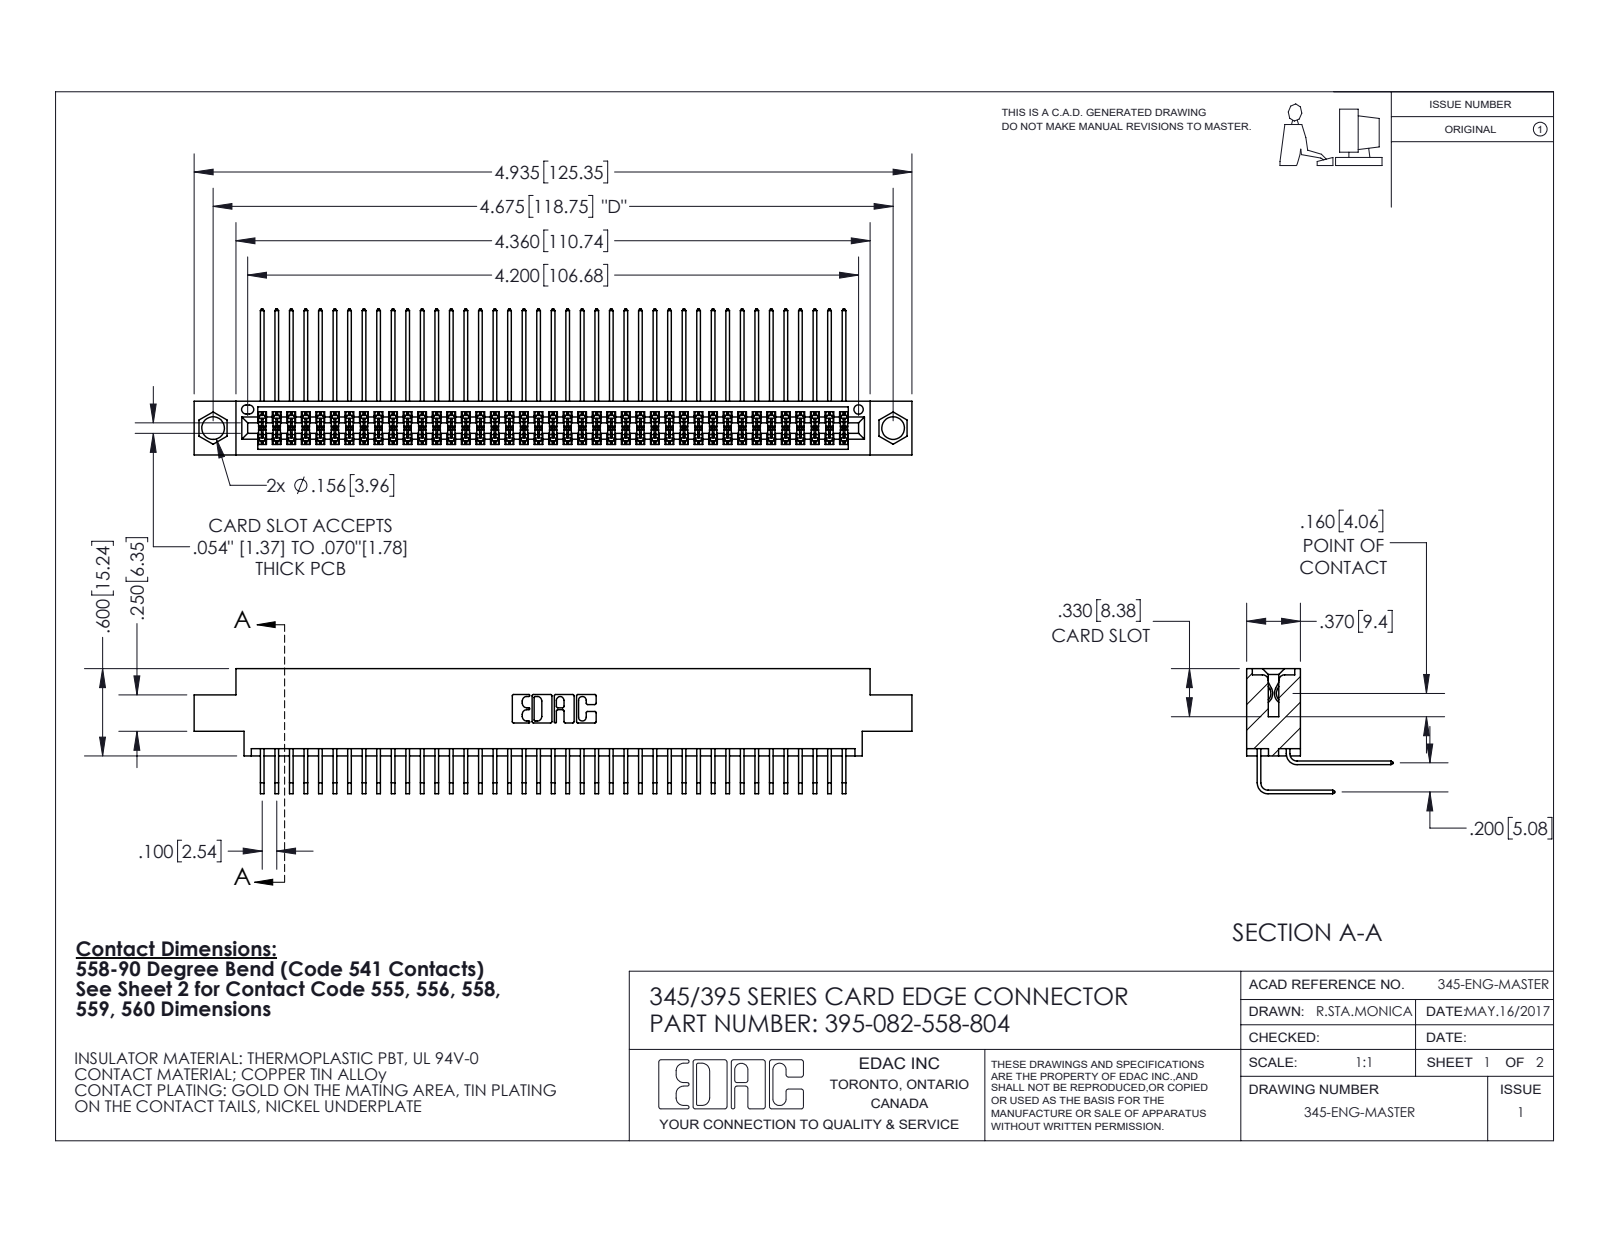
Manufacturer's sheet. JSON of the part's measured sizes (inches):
{"part_name": "345-292-001_558 559 Tail - 1; 395-082-558-804; 345 Part_0.170 Offset - 0.156 Dia-TI; 345-292-001_558 Tail - 2", "step_written_by": "SolidWorks 2020 (CONFIG_CONTROL_DESIGN)", "units": "inches", "bodies": {"solids": 83, "faces": 4408, "planar": 2968, "cylindrical": 1440, "other": 0}, "overall_size": [4.935, 1.005, 0.859], "volume_in3": 0.758, "surface_area_in2": 31.87, "round_holes": [[0.156, 2], [0.064, 1]], "partial_cylinders_radius": [[0.006, 123], [0.01, 22], [0.007, 6], [0.031, 6], [0.026, 3], [0.014, 2], [0.019, 2], [0.022, 2]], "face_to_face_distances": [0.072, 0.298, 0.2, 0.37, 0.098, 0.272, 0.025, 0.225, 0.175, 0.025], "hole_center_spacings": [0.27, 4.439, 4.675]}
